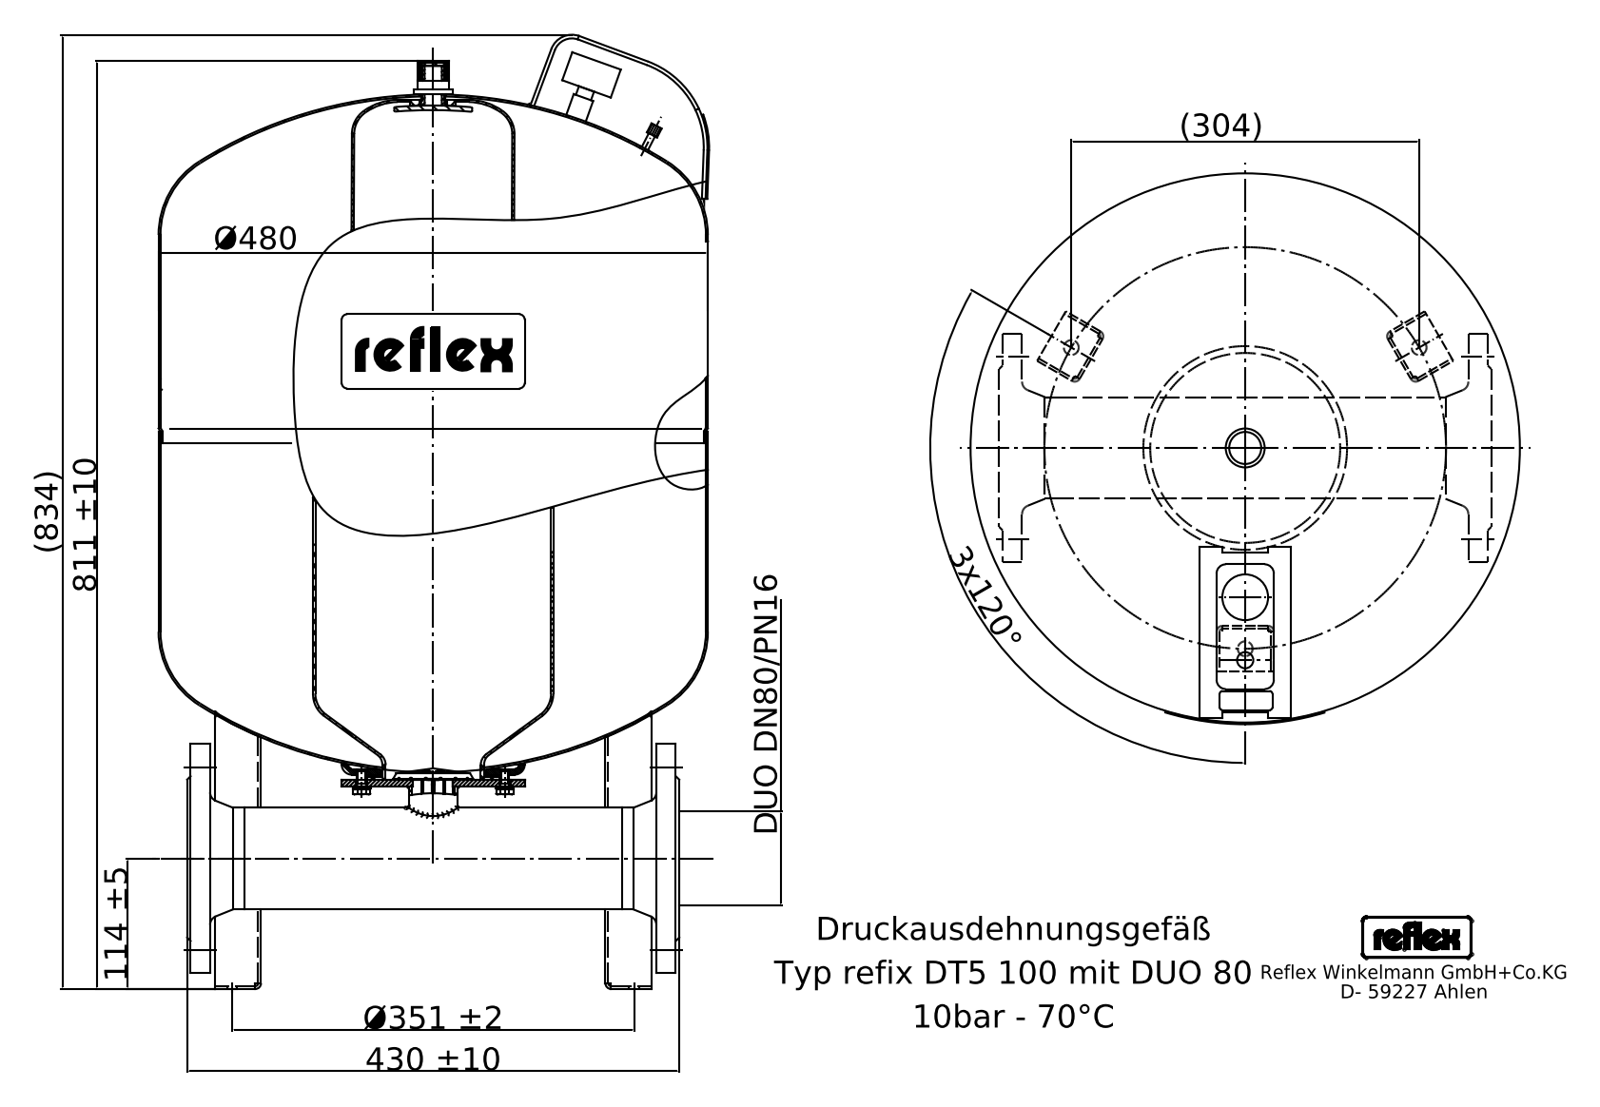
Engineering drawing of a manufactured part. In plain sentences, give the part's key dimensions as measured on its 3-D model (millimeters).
Its 3-D file was written by "Mechanical Desktop 2008 (CONFIG_CONTROL_DESIGN)". It is 23 solids with 549 faces: 226 planar, 197 cylindrical and 126 other. Overall it measures 828.24 by 480 by 480 millimeters. Its volume is 94 570 000 cubic millimeters and its surface area 2 391 000 square millimeters. Round holes: 8 of diameter 19, 3 of diameter 13.4, 1 of diameter 2.48, 1 of diameter 3.8, 1 of diameter 4.3, 1 of diameter 4.4, 1 of diameter 5.45, 1 of diameter 7, 1 of diameter 8, 1 of diameter 11.4, 1 of diameter 88.9, 1 of diameter 92. Round bosses or shafts: 9 of diameter 10, 1 of diameter 480, 1 of diameter 200, 1 of diameter 160, 1 of diameter 140, 1 of diameter 62, 1 of diameter 42.4, 1 of diameter 34. Partial cylindrical surfaces (rounded edges, fillets, slot ends): 15 of radius 1, 15 of radius 2.5, 15 of radius 5, 4 of radius 3.94, 3 of radius 1.57, 2 of radius 2.69, 2 of radius 4.72, 2 of radius 6.49. The main face-to-face distances are 323, 2.5, 47.5, 50, 45, 141, 464, 6, 147, 470. The hole center spacings are 80, 113.13, 61.22, 61.24, 147.81, 147.82, 160, 175.5.
